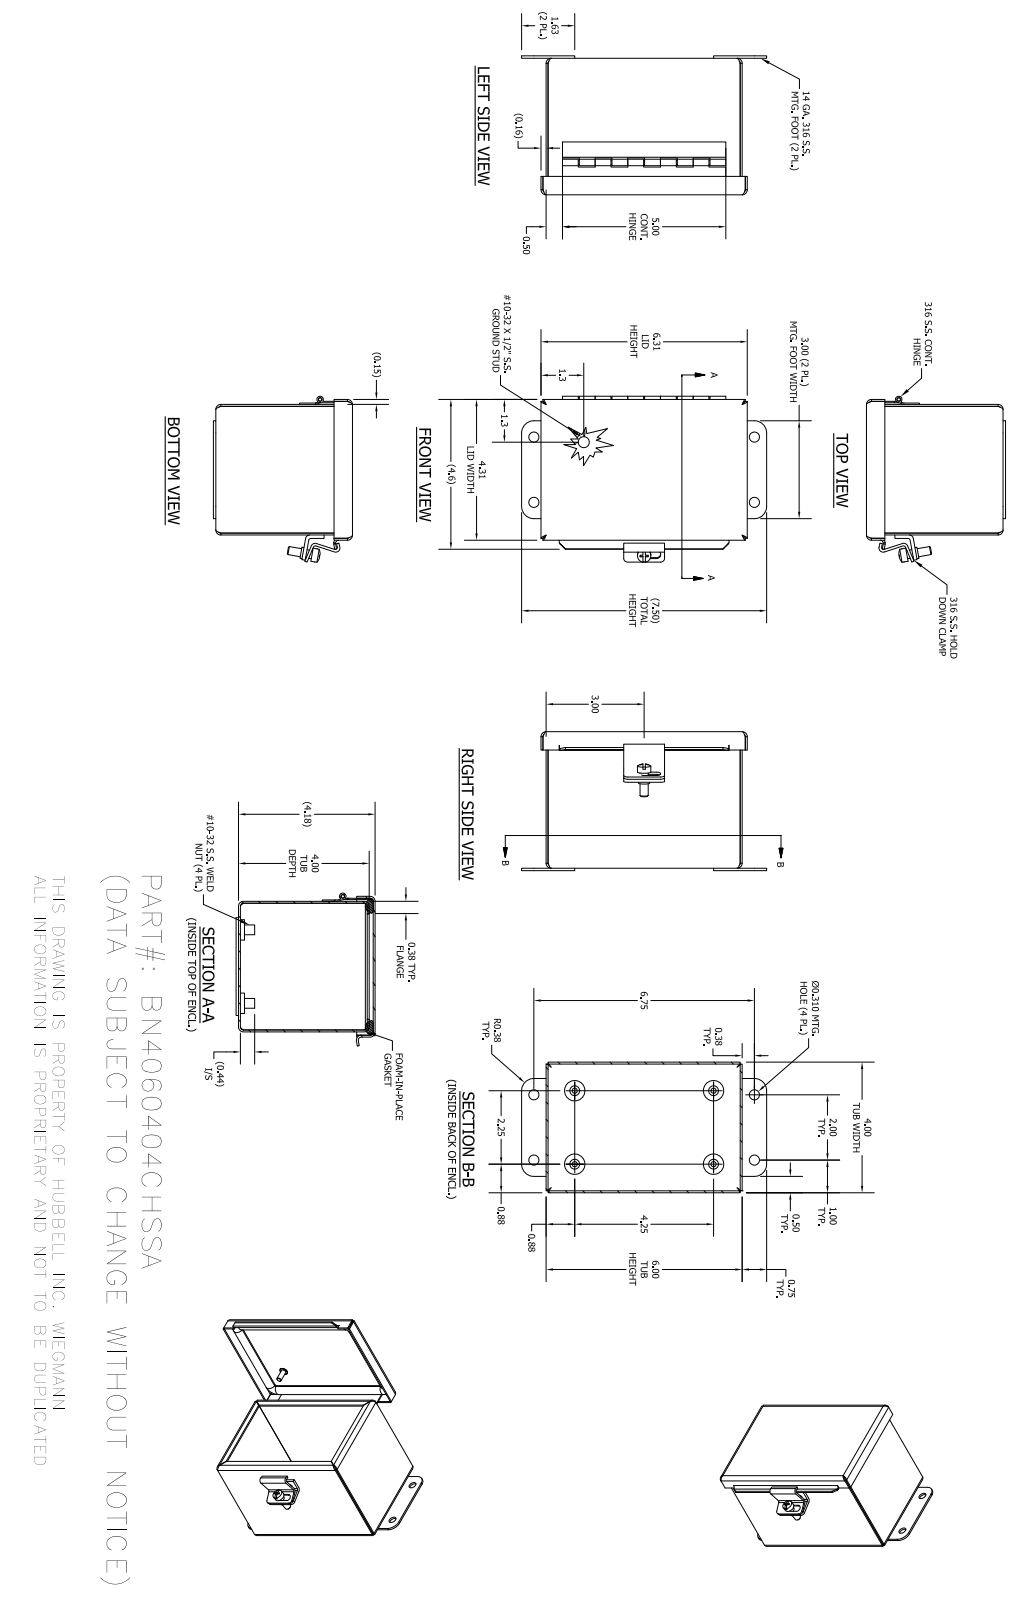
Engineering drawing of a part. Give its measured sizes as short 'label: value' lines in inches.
name: B_060404_SSABKP; 32882LH; 32882P; 32882TH (+8 more)
written by: Autodesk Inventor 2016 (AUTOMOTIVE_DESIGN)
unit: in
bodies: 16 solids, 343 faces (182 planar, 101 cylindrical, 60 other)
size: 7.5 × 5.086 × 4.256
volume: 11.65 in³; area: 365.5 in²
holes: 4× ⌀0.156, 4× ⌀0.31, 2× ⌀0.11, 1× ⌀0.117, 1× ⌀0.196
bosses: 4× ⌀0.625, 4× ⌀0.3, 1× ⌀0.409, 1× ⌀0.344, 1× ⌀0.337, 1× ⌀0.25, 1× ⌀0.2, 1× ⌀0.19
rounds: 13× R0.094, 13× R0.153, 8× R0.066, 4× R0.125, 4× R0.228, 4× R0.375, 3× R0.063, 3× R0.126
face distances: 0.059, 4.122, 3.941, 5.941, 4, 3.882, 4.181, 4.063, 6, 5.882
hole spacings: 2.466, 1.256, 5.501, 5.896, 2, 2.25, 4.25, 4.809
